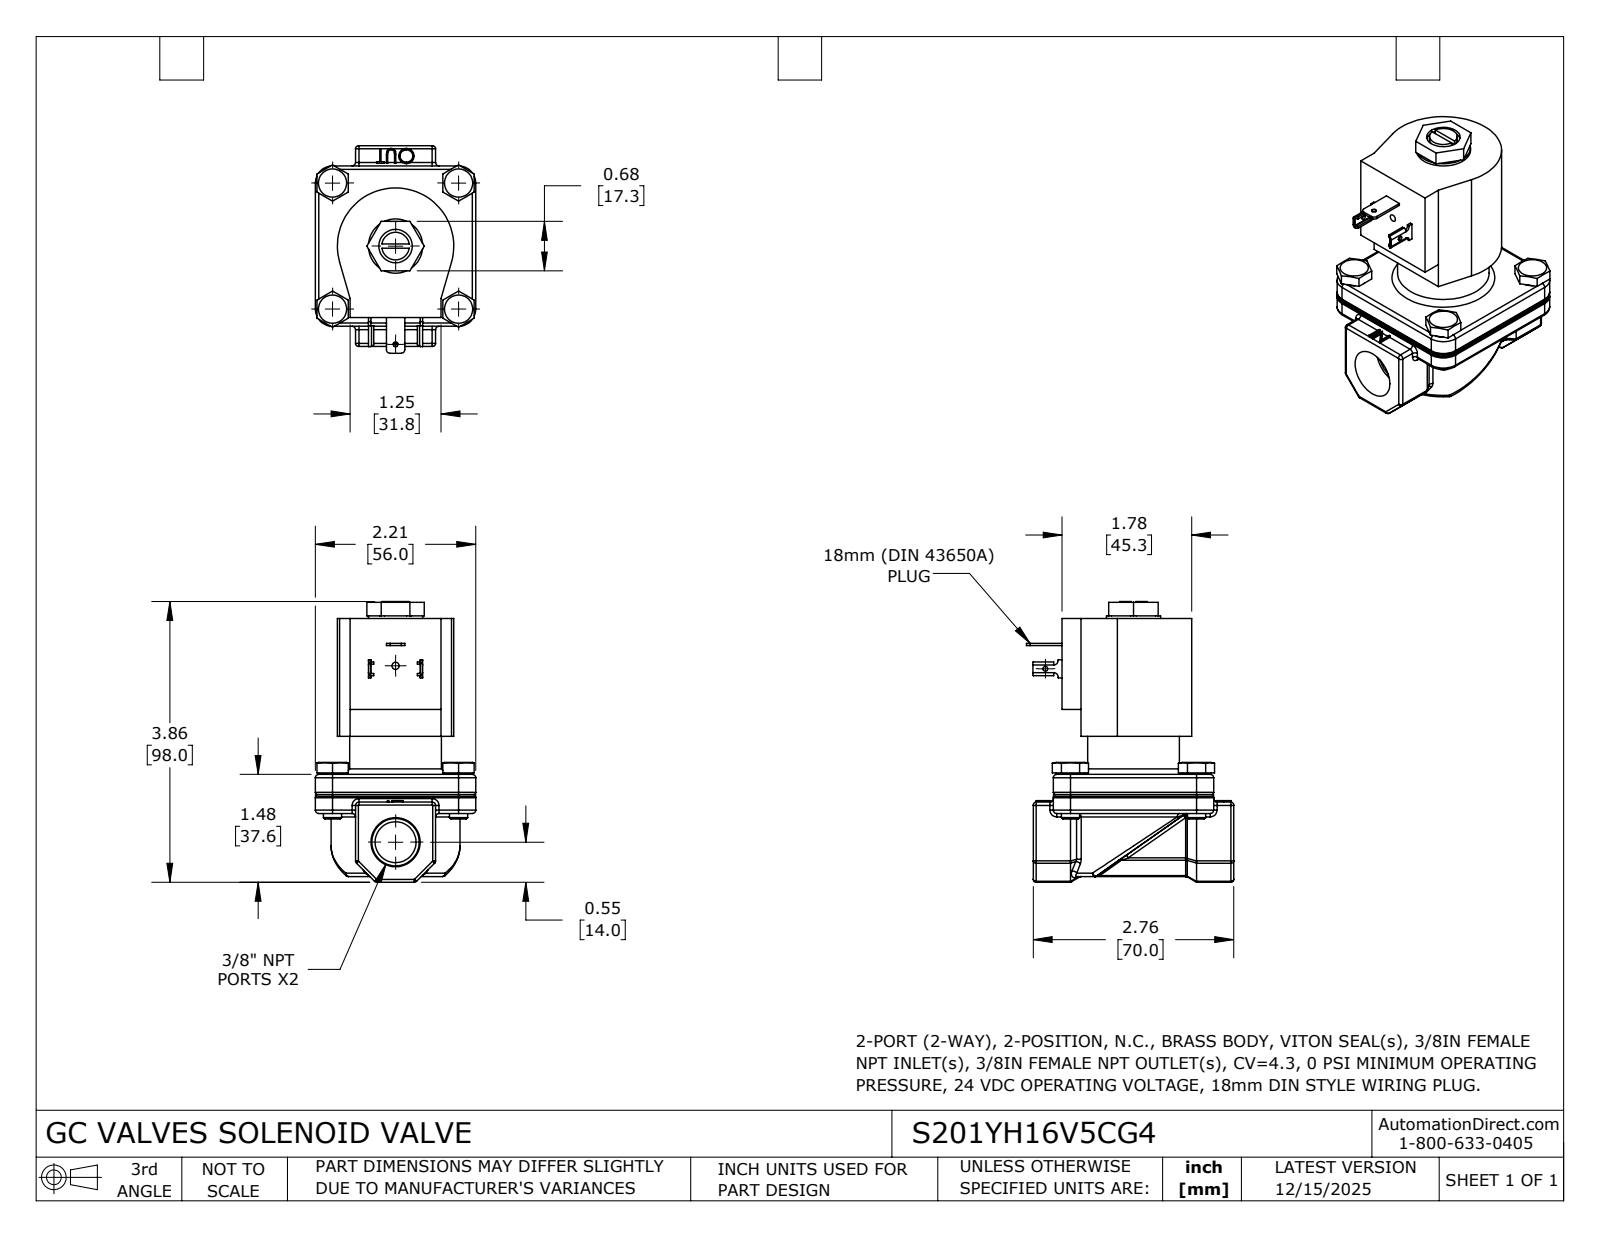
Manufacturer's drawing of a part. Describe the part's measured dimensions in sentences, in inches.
The part is named "S201YH16V5CG4". Its 3-D file was written by "SolidWorks 2024 (CONFIG_CONTROL_DESIGN)". It is 1 solid with 483 faces: 204 planar, 153 cylindrical and 126 other. Overall it measures 3.857 by 2.851 by 2.205 inches. Its volume is 9.705 cubic inches and its surface area 40.43 square inches. Round holes: 1 of diameter 0.066, 1 of diameter 0.067, 1 of diameter 0.1, 1 of diameter 0.46, 1 of diameter 0.562. Round bosses or shafts: 4 of diameter 0.388, 4 of diameter 0.25, 1 of diameter 1.26, 1 of diameter 0.746, 1 of diameter 0.38. Partial cylindrical surfaces (rounded edges, fillets, slot ends): 57 of radius 0.047, 12 of radius 0.04, 4 of radius 0.006, 4 of radius 0.031, 4 of radius 0.041, 4 of radius 0.234, 4 of radius 0.236, 2 of radius 0.05. The main face-to-face distances are 2.143, 0.551, 1.654, 2.205, 0.537, 2.68, 0.276, 2.48, 1.06, 0.523. The hole center spacings are 1.35, 2.423.
